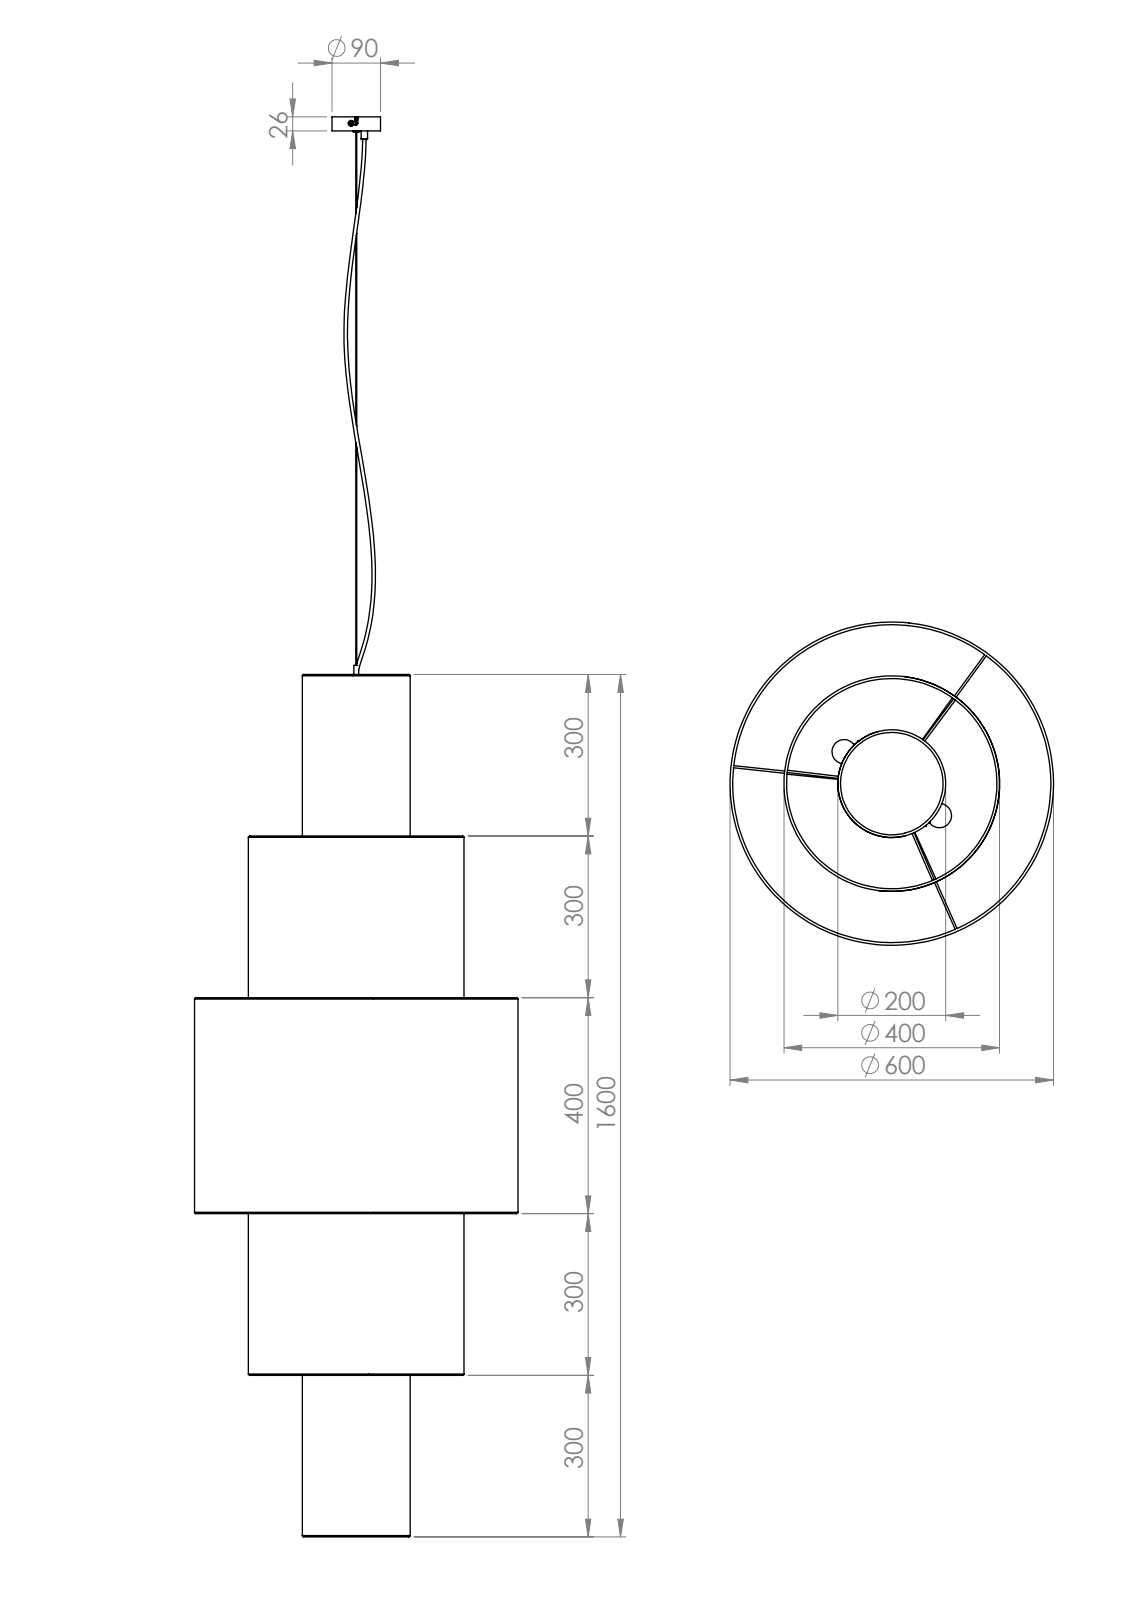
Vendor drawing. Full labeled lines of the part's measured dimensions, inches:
Part name (STEP PRODUCT): Swivel joint_90deg; FLY SC060160 kuppel D600; Swivel joint 1; FLY SC080220 kuppel D400 (+8 more)
STEP written by: SolidWorks 2018 (AUTOMOTIVE_DESIGN)
Units: inches
Bodies: 56 solids, 607 faces (190 planar, 225 cylindrical, 192 other)
Overall size (bounding box): 103.78 × 23.622 × 23.622
Volume: 135.7 in³ · Surface area: 7 390 in²
Round holes (diameter × count): ⌀0.354 ×6, ⌀1.063 ×4, ⌀0.315 ×3, ⌀0.353 ×2, ⌀0.098 ×1, ⌀0.197 ×1, ⌀0.394 ×1, ⌀3.386 ×1, ⌀7.835 ×1, ⌀15.709 ×1, ⌀23.583 ×1
Round bosses / shafts (diameter × count): ⌀0.157 ×12, ⌀1.575 ×4, ⌀0.315 ×4, ⌀0.63 ×3, ⌀0.236 ×3, ⌀0.472 ×2, ⌀0.413 ×2, ⌀23.622 ×1
Partial cylindrical surfaces — rounded edges, fillets, slot ends (radius × count): R0.197 ×10, R0.118 ×5, R0.079 ×4, R0.315 ×4, R0.029 ×2, R0.108 ×2
Main face-to-face distances: 0.157, 62.52, 62.677, 62.362, 30.551, 32.126, 30.394, 31.969, 0.079, 102.579
Hole centre spacings: 2.333, 4.666, 0.591, 1.181, 1.743, 2.924
